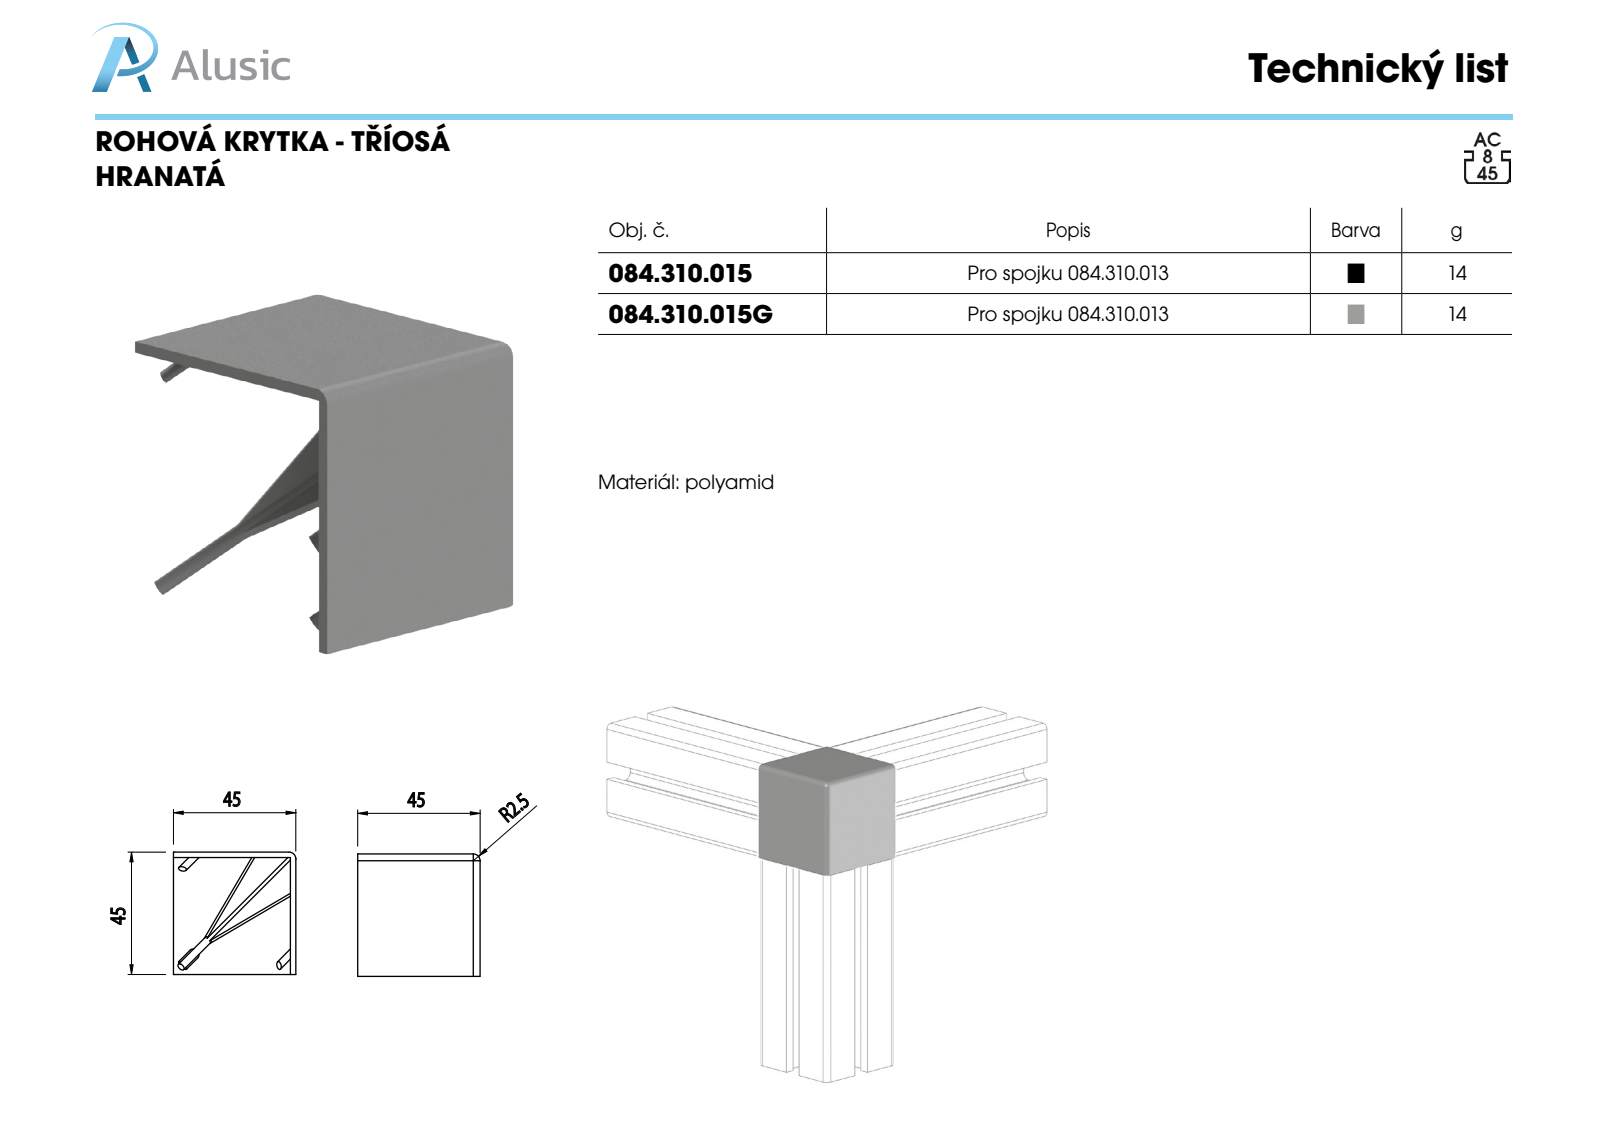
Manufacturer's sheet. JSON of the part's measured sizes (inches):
{"part_name": "084.310.015", "step_written_by": "SolidWorks 2011 (CONFIG_CONTROL_DESIGN)", "units": "inches", "bodies": {"solids": 1, "faces": 52, "planar": 46, "cylindrical": 5, "other": 1}, "overall_size": [1.772, 1.772, 1.772], "volume_in3": 0.805, "surface_area_in2": 22.12, "round_bosses_or_shafts": [[0.11, 1]], "partial_cylinders_radius": [[0.098, 3]], "face_to_face_distances": [0.079, 0.059, 1.772, 1.693, 0.049, 0.108, 0.157, 0.866]}
